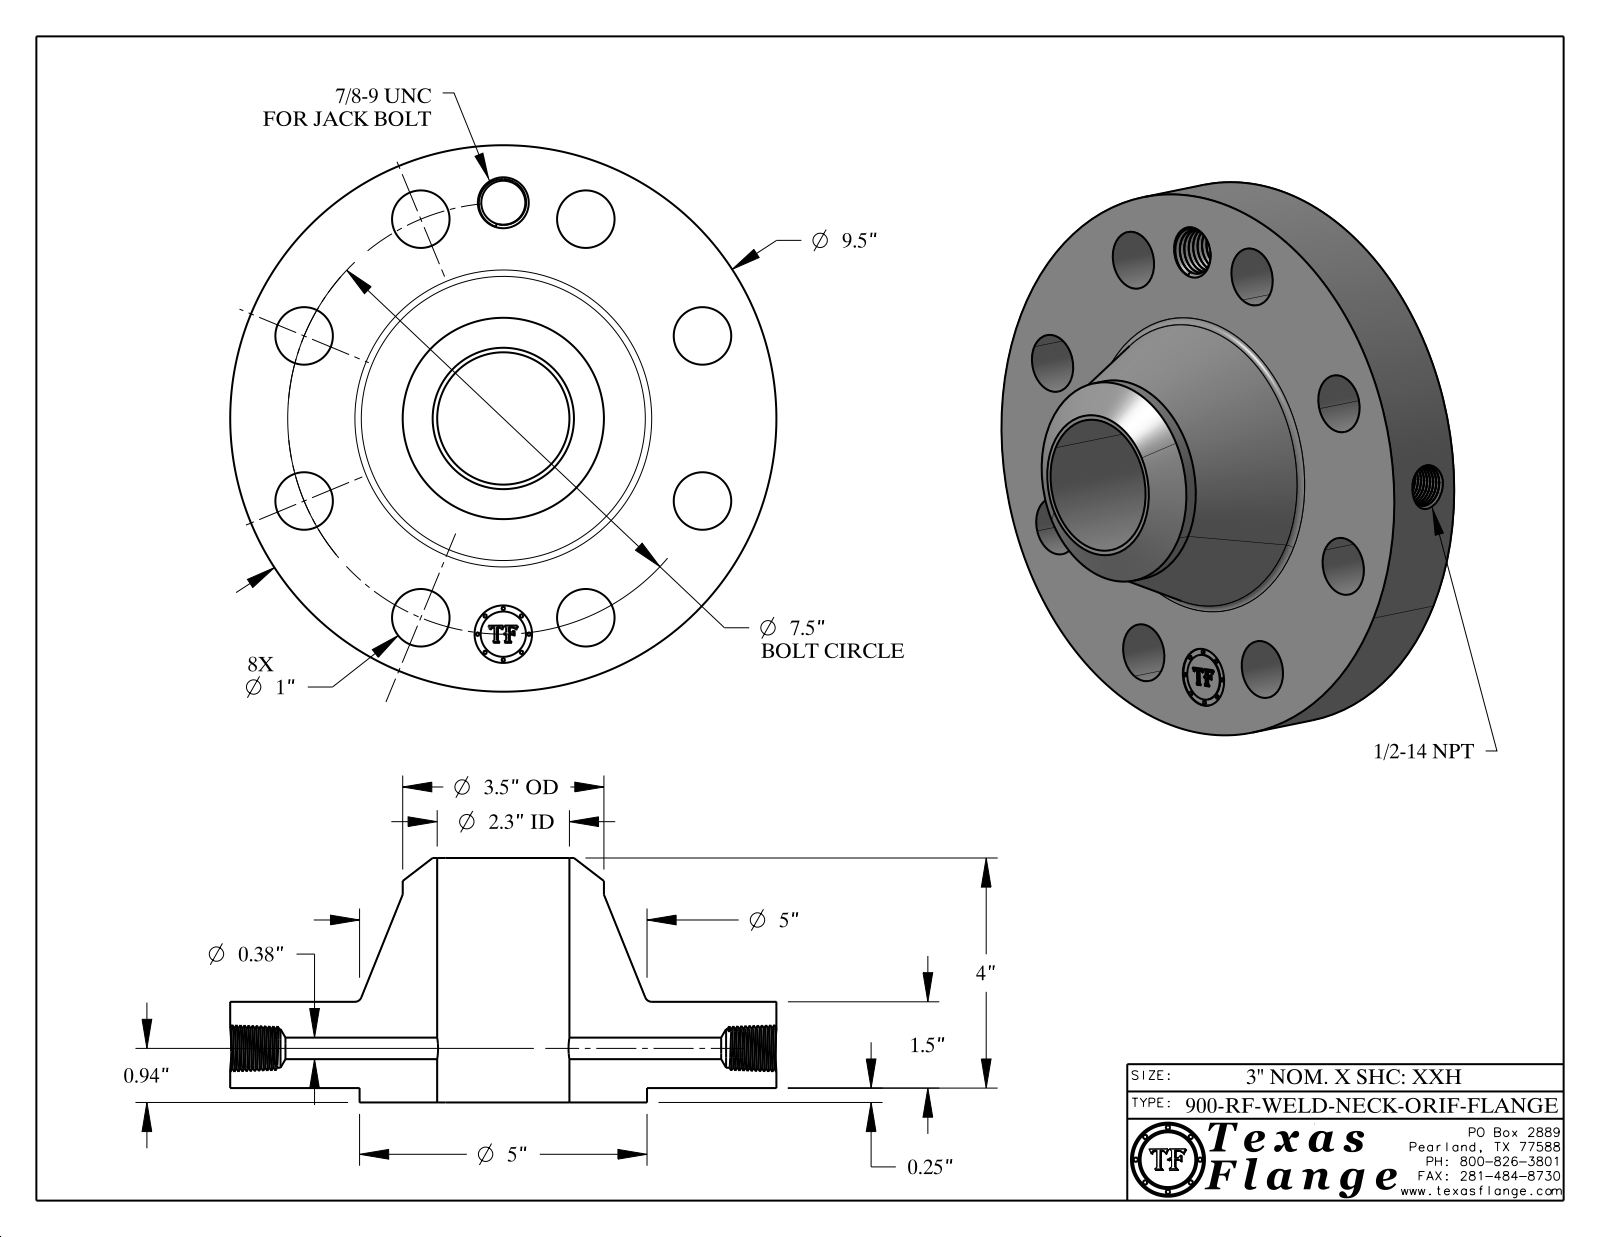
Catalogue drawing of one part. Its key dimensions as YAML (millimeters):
part_name: "900-RF-WELD-NECK"
step_written_by: "CATIA V5 STEP AP214 (AUTOMOTIVE_DESIGN)"
units: millimeters
bodies: {solids: 1, faces: 759, planar: 369, cylindrical: 90, other: 300}
overall_size: [241.3, 241.3, 108]
volume: 1865000
surface_area: 177900
round_holes:
  - {diameter: 25.4, count: 9}
  - {diameter: 9.5, count: 1}
  - {diameter: 17.1, count: 1}
  - {diameter: 19.5, count: 1}
  - {diameter: 58.4, count: 1}
round_bosses_or_shafts:
  - {diameter: 1.5, count: 8}
  - {diameter: 241.3, count: 1}
  - {diameter: 127, count: 1}
  - {diameter: 88.9, count: 1}
  - {diameter: 20, count: 1}
face_to_face_distances: [38.1, 6.4, 44.5, 108, 101.6, 63.5, 44.1, 37.7, 0.4, 63.9]
hole_center_spacings: [95.3, 72.9, 134.7, 176, 190.5, 37.2, 105.8, 158.4]
